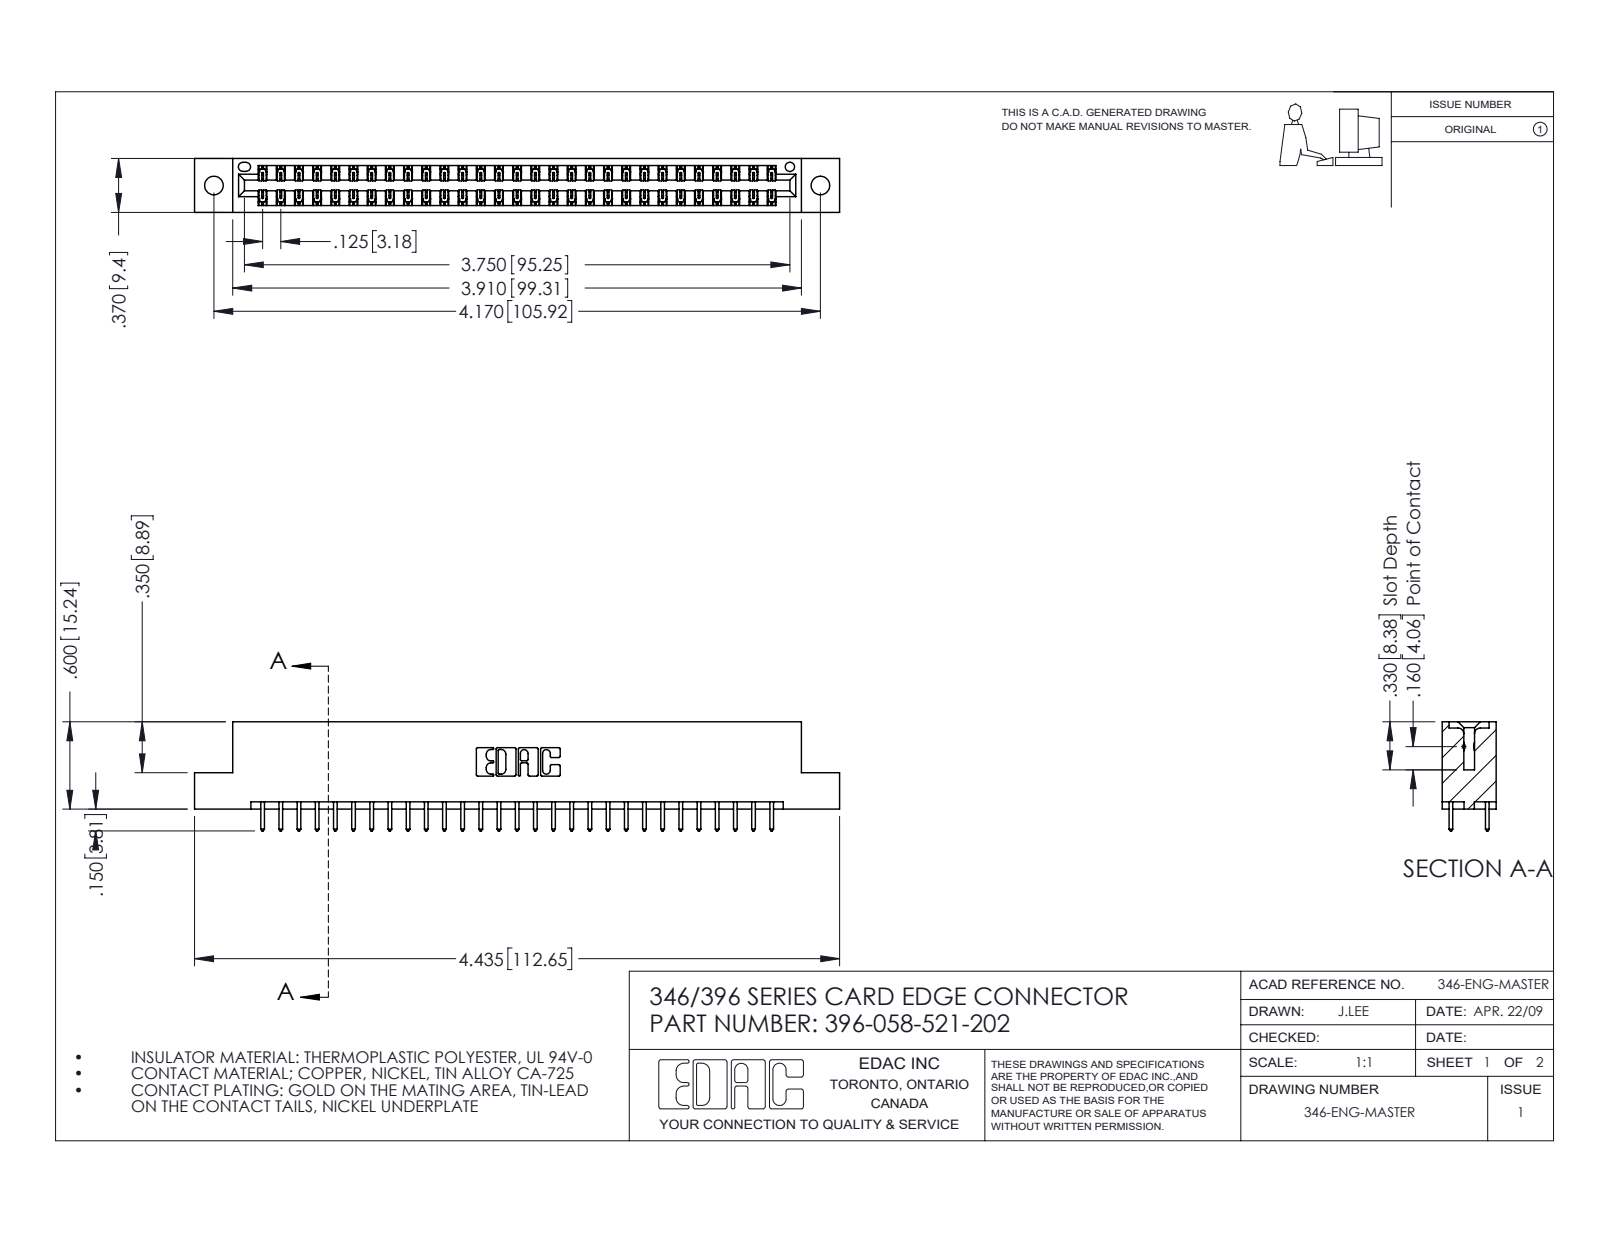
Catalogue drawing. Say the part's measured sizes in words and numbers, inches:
The part is named "396-058-521-202; 346 Part_Flush Mounting Lugs - 0.128 Dia; 345-292-001_345-293-121". Its 3-D file was written by "SolidWorks 2016 (CONFIG_CONTROL_DESIGN)". It is 59 solids with 3138 faces: 2106 planar, 1032 cylindrical and 0 other. Overall it measures 4.435 by 0.75 by 0.37 inches. Its volume is 0.66 cubic inches and its surface area 22.08 square inches. Round holes: 2 of diameter 0.128, 1 of diameter 0.064. Partial cylindrical surfaces (rounded edges, fillets, slot ends): 87 of radius 0.006, 58 of radius 0.01, 22 of radius 0.01, 6 of radius 0.007, 6 of radius 0.031, 3 of radius 0.026, 2 of radius 0.014, 2 of radius 0.022. The main face-to-face distances are 0.048, 0.322, 0.25, 0.37, 0.072, 0.298, 0.025, 0.275, 0.148, 0.222. The hole center spacings are 0.246, 3.962, 4.17.
